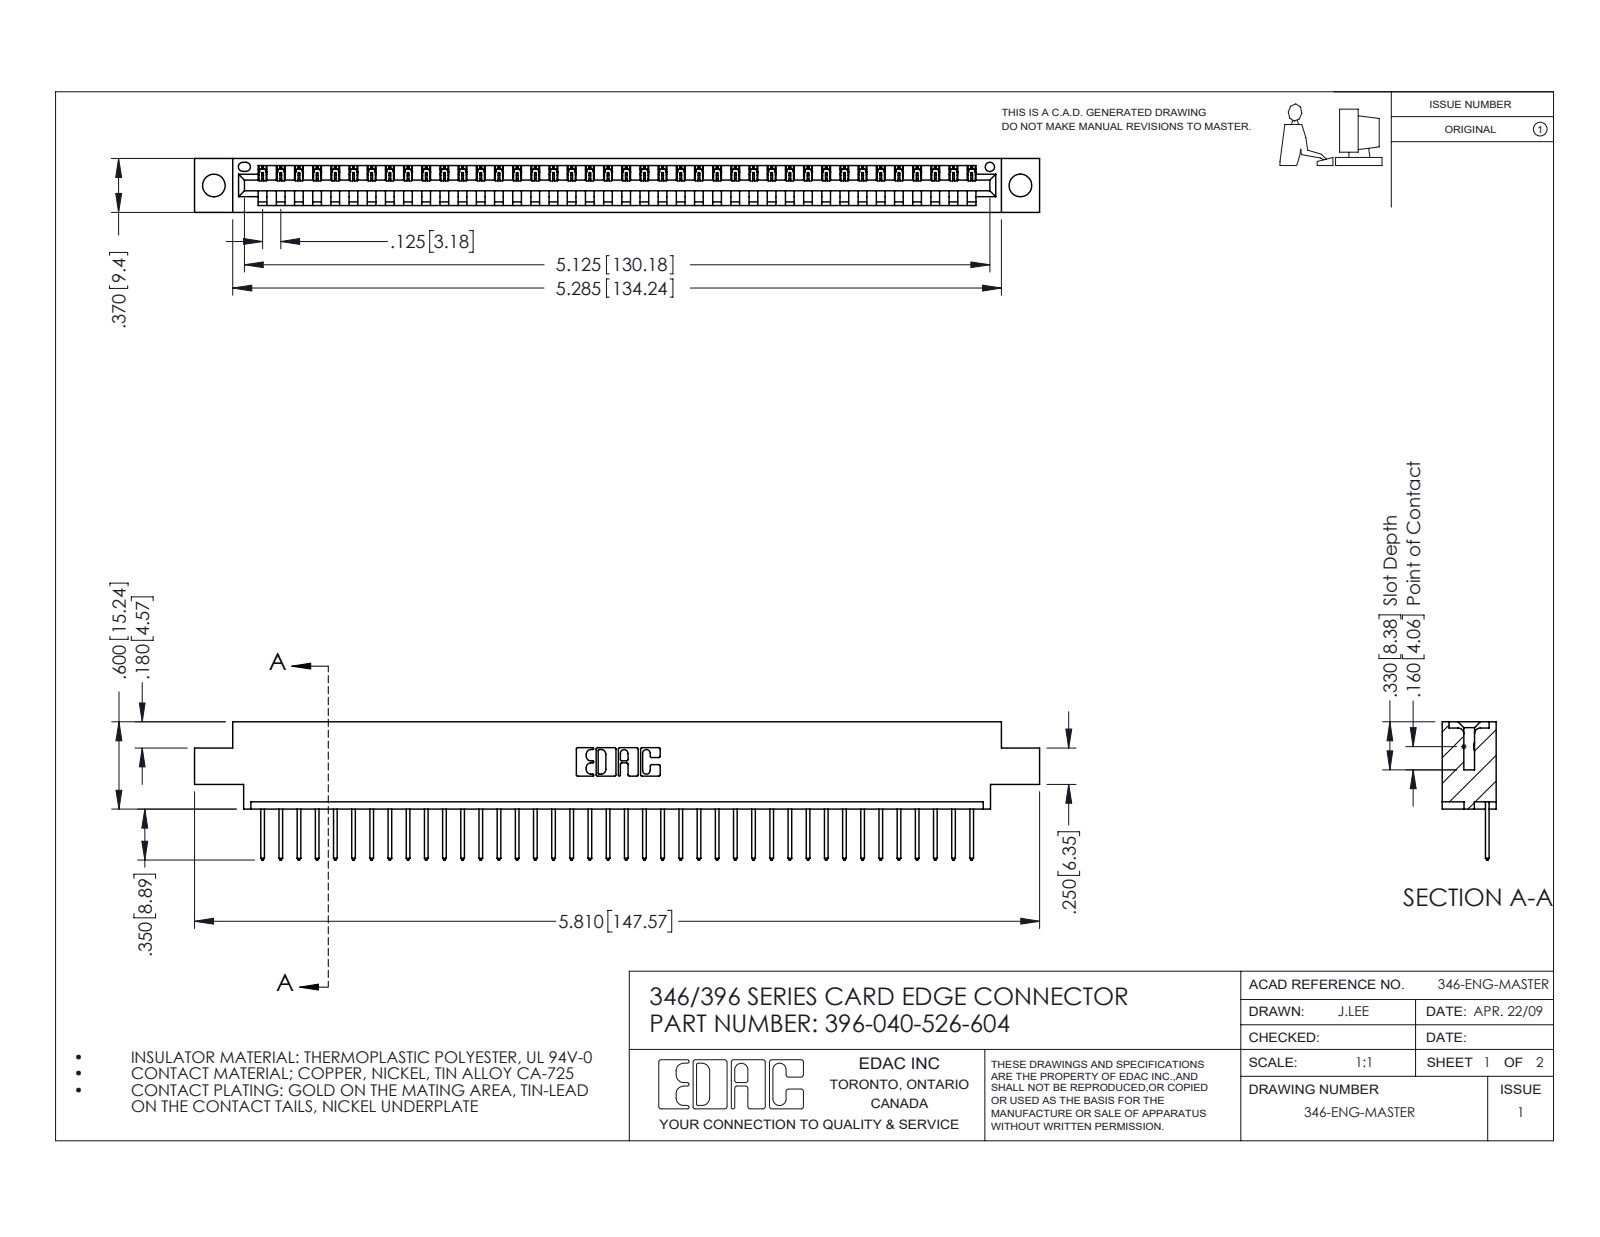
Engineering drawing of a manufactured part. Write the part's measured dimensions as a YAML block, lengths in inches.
part_name: "346 Part_0.170 Offset - 0.156 Dia-TH; 396-040-526-604; 345-292-001_345-293-126"
step_written_by: "SolidWorks 2016 (CONFIG_CONTROL_DESIGN)"
units: inches
bodies: {solids: 41, faces: 2446, planar: 1680, cylindrical: 766, other: 0}
overall_size: [5.81, 0.95, 0.37]
volume: 0.844
surface_area: 26.66
round_holes:
  - {diameter: 0.156, count: 2}
  - {diameter: 0.064, count: 1}
partial_cylinders:
  - {radius: 0.006, count: 80}
  - {radius: 0.01, count: 80}
  - {radius: 0.01, count: 22}
  - {radius: 0.007, count: 6}
  - {radius: 0.031, count: 6}
  - {radius: 0.026, count: 3}
  - {radius: 0.031, count: 2}
  - {radius: 0.04, count: 2}
face_to_face_distances: [0.048, 0.322, 0.37, 0.25, 0.072, 0.298, 0.025, 0.148, 0.222, 0.1]
hole_center_spacings: [0.246, 5.336, 5.545]
